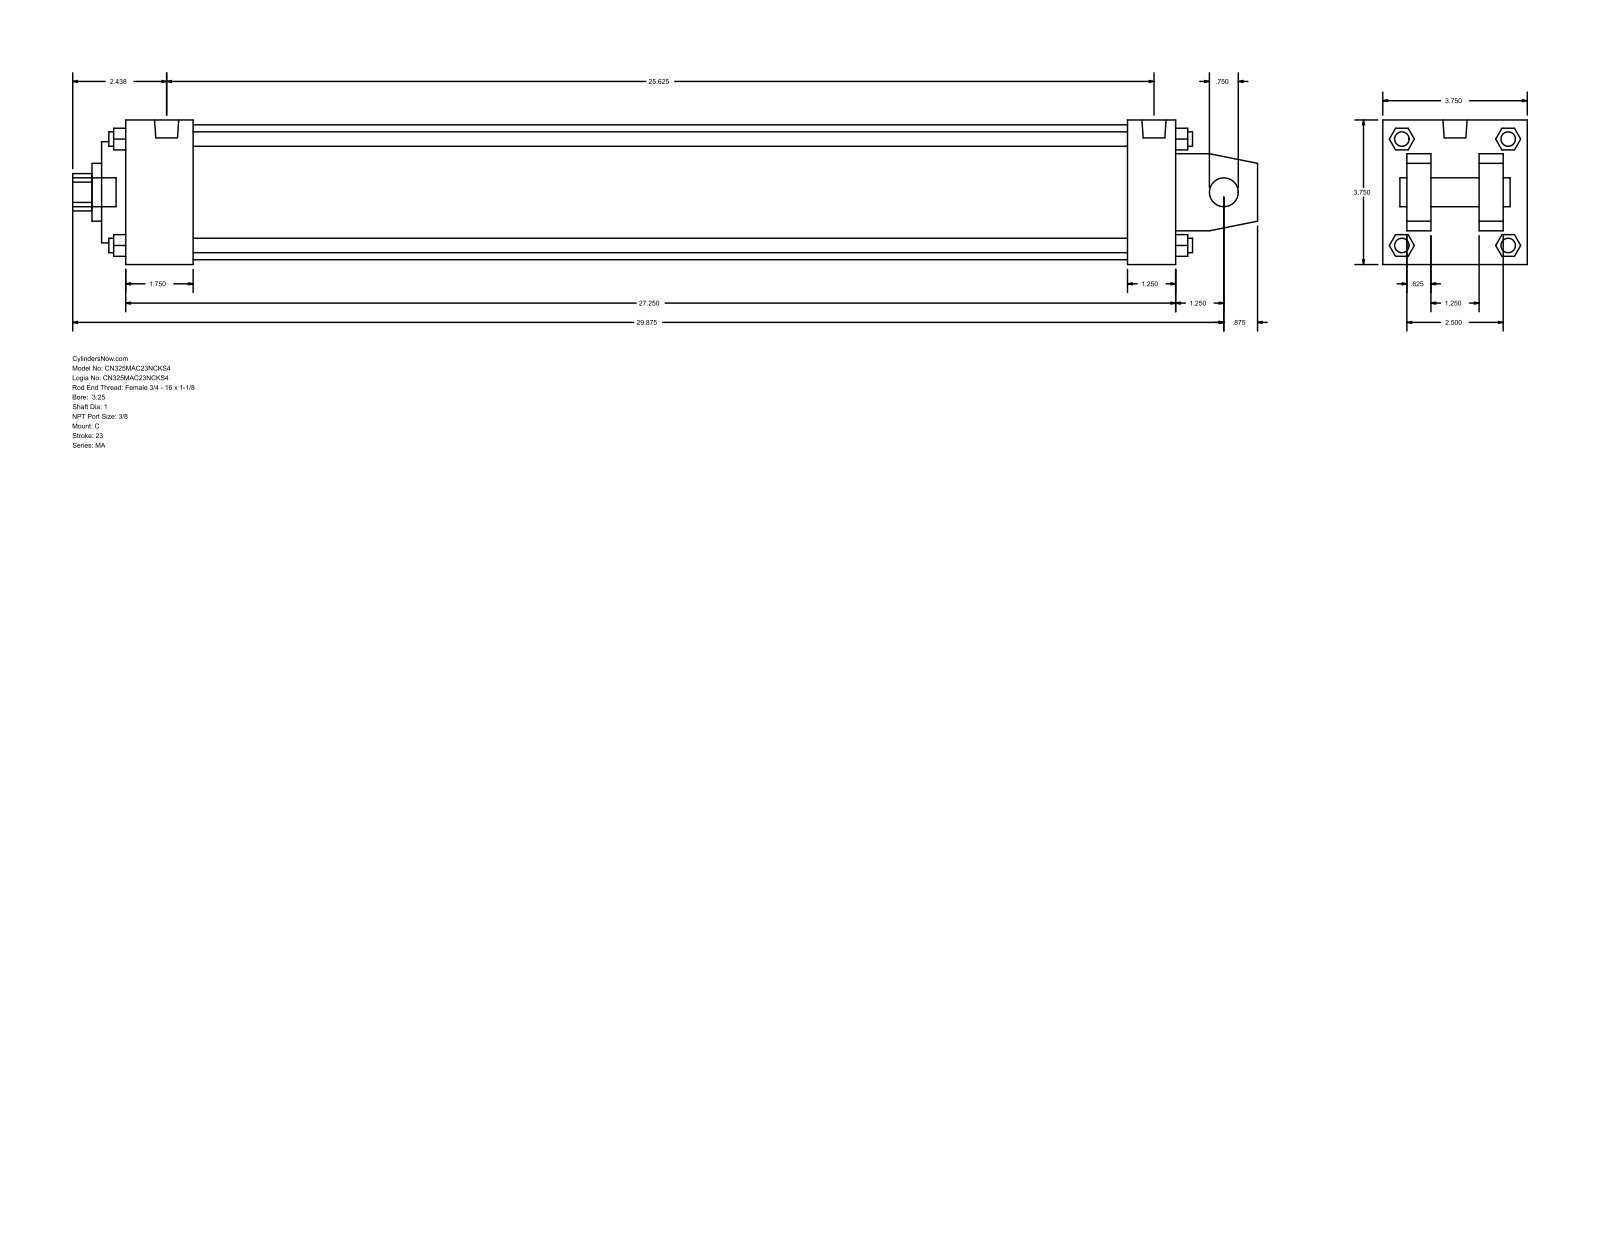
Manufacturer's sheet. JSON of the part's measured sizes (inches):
{"part_name": "MA_C__0325_1", "step_written_by": "GSSL Pune (CONFIG_CONTROL_DESIGN)", "units": "inches", "bodies": {"solids": 0, "faces": 141, "planar": 109, "cylindrical": 32, "other": 0}, "overall_size": [30.75, 3.75, 3.75], "round_holes": [[0.75, 1], [1, 1], [1.5, 1], [2.625, 1], [3.5, 1]], "round_bosses_or_shafts": [[0.437, 4], [0.375, 4], [0.627, 2], [0.75, 1]], "partial_cylinders_radius": [[0.484, 1]], "face_to_face_distances": [3.75, 0.625, 2.5, 27.25, 1.25, 3.125, 1.875, 26, 1.25, 1.75]}
